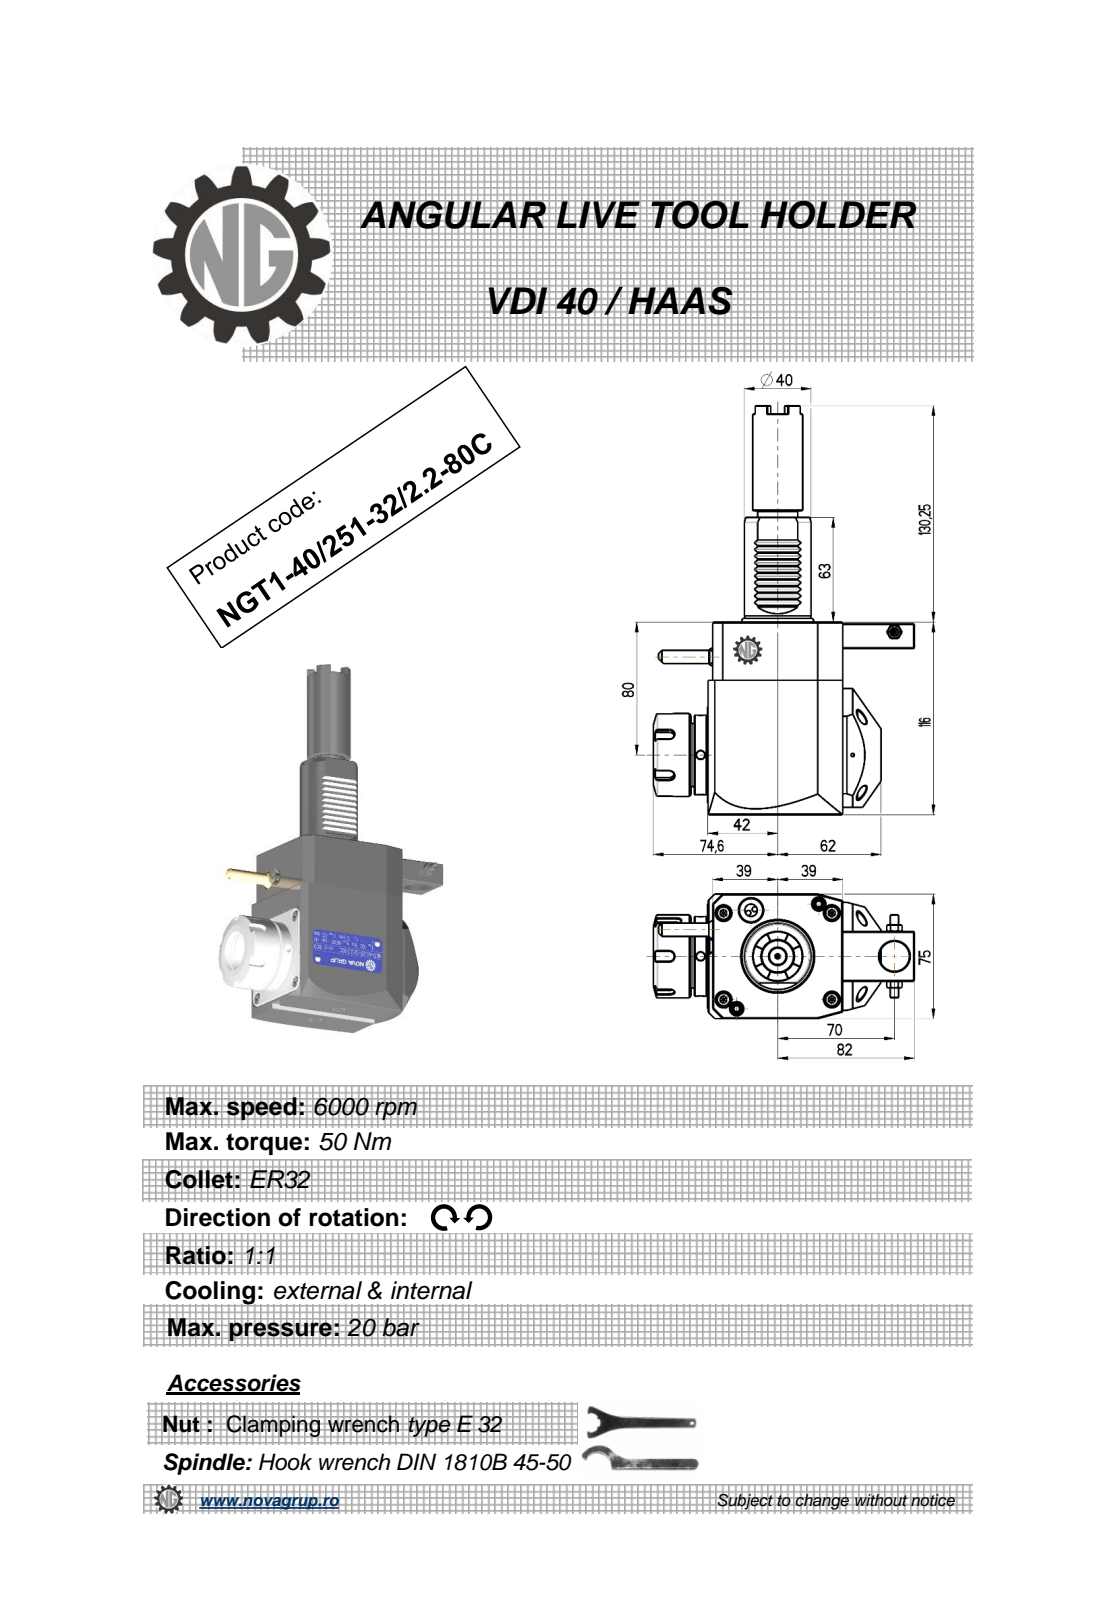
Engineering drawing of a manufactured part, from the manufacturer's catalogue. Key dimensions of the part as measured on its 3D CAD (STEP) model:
Part name (STEP PRODUCT): NGT1_40_251_32_2_2_80C
STEP written by: PRO/ENGINEER BY PARAMETRIC TECHNOLOGY CORPORATION, 2010280 (CONFIG_CONTROL_DESIGN)
Units: millimetres
Bodies: 1 solid, 459 faces (226 planar, 92 cylindrical, 141 other)
Overall size (bounding box): 246.25 × 156.6 × 76.6
Volume: 936 343 mm³ · Surface area: 79 563 mm²
Round holes (diameter × count): ⌀5 ×3, ⌀3 ×1, ⌀4.2 ×1, ⌀9.5 ×1, ⌀18 ×1, ⌀19.5 ×1, ⌀27 ×1
Round bosses / shafts (diameter × count): ⌀50 ×1, ⌀48 ×1, ⌀41 ×1, ⌀40 ×1, ⌀30 ×1, ⌀24 ×1, ⌀10 ×1, ⌀8.96 ×1
Partial cylindrical surfaces — rounded edges, fillets, slot ends (radius × count): R0.26 ×12, R0.3 ×10, R0.2 ×6, R3 ×5, R0.5 ×1, R40 ×1
Main face-to-face distances: 75, 116, 81, 3, 78, 2.8, 80.8, 1, 22.5, 112
Hole centre spacings: 20.93, 46.25, 61.13, 70, 72.5, 116.25, 137.8
